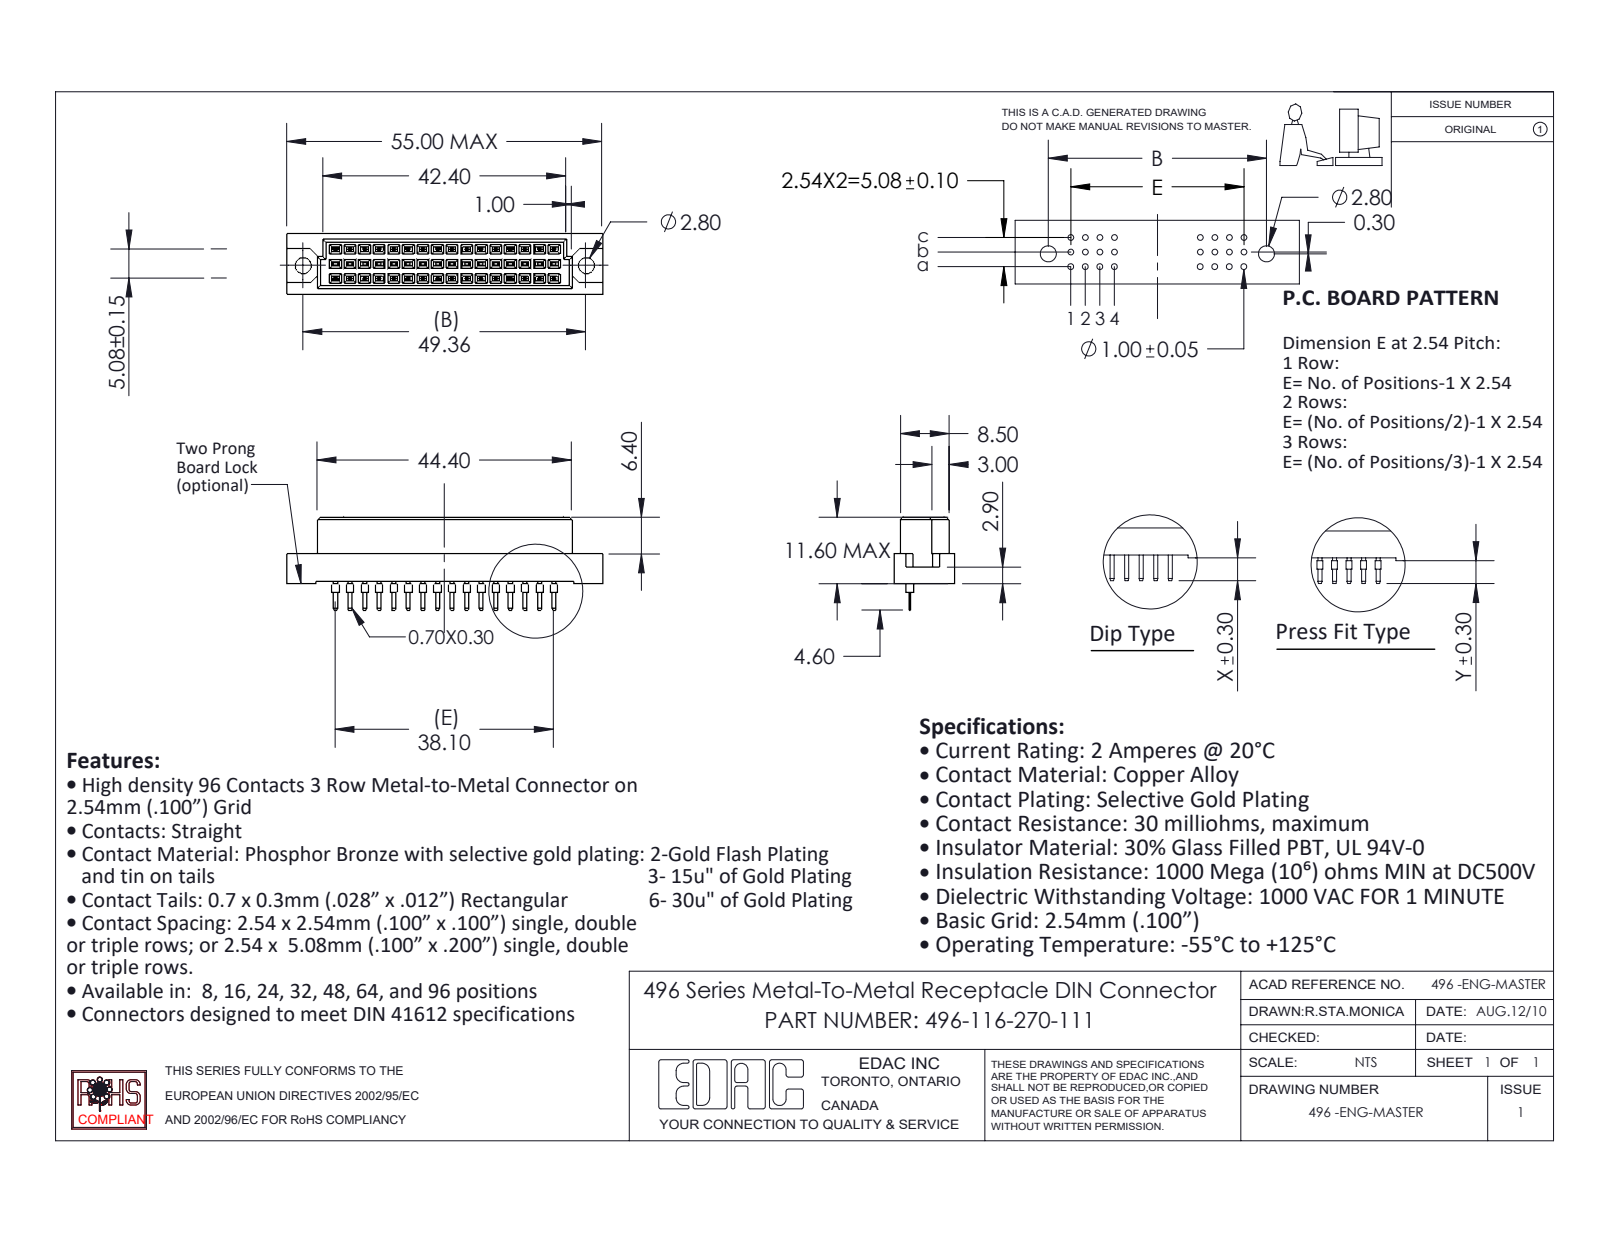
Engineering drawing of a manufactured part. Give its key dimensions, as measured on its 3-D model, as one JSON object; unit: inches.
{"part_name": "496-116-270-111; 496 Part_48; 496-290_70", "step_written_by": "SolidWorks 2020 (CONFIG_CONTROL_DESIGN)", "units": "inches", "bodies": {"solids": 17, "faces": 954, "planar": 918, "cylindrical": 36, "other": 0}, "overall_size": [2.165, 0.638, 0.417], "volume_in3": 0.283, "surface_area_in2": 7.056, "round_holes": [[0.11, 2]], "round_bosses_or_shafts": [[0.039, 16]], "face_to_face_distances": [0.1, 0.2, 0.041, 0.376, 0.032, 0.417, 0.132, 0.068, 0.335, 0.022], "hole_center_spacings": [1.943]}
